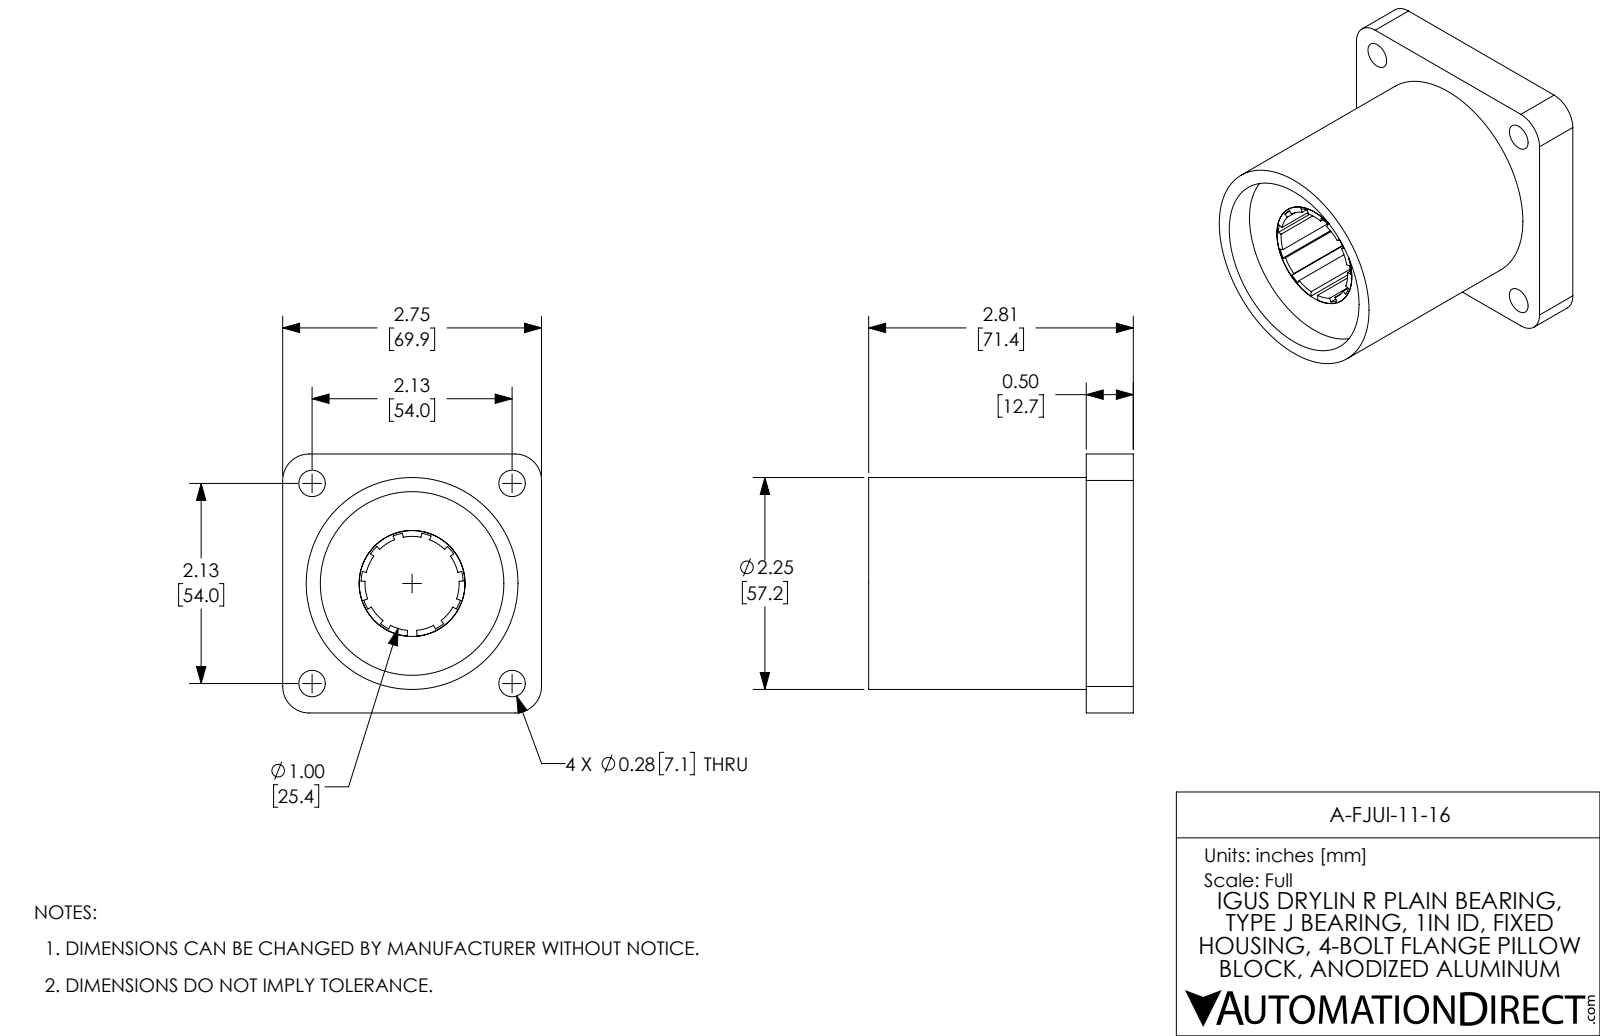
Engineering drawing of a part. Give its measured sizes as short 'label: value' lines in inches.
name: A-FJUI-11-16
written by: SolidWorks 2017 (AUTOMOTIVE_DESIGN)
unit: in
bodies: 2 solids, 135 faces (76 planar, 59 cylindrical, 0 other)
size: 2.812 × 2.75 × 2.75
volume: 9.178 in³; area: 64.64 in²
holes: 4× ⌀0.281, 1× ⌀1.95
bosses: 1× ⌀2.25, 1× ⌀1.125, 1× ⌀0.15
rounds: 4× R0.281, 1× R0.5, 1× R0.543, 1× R0.594
face distances: 0.5, 2.508, 0.304, 2.75, 2.008, 0.196, 2.205, 2.812, 2.312, 1.312
hole spacings: 1.503, 2.125, 3.006
